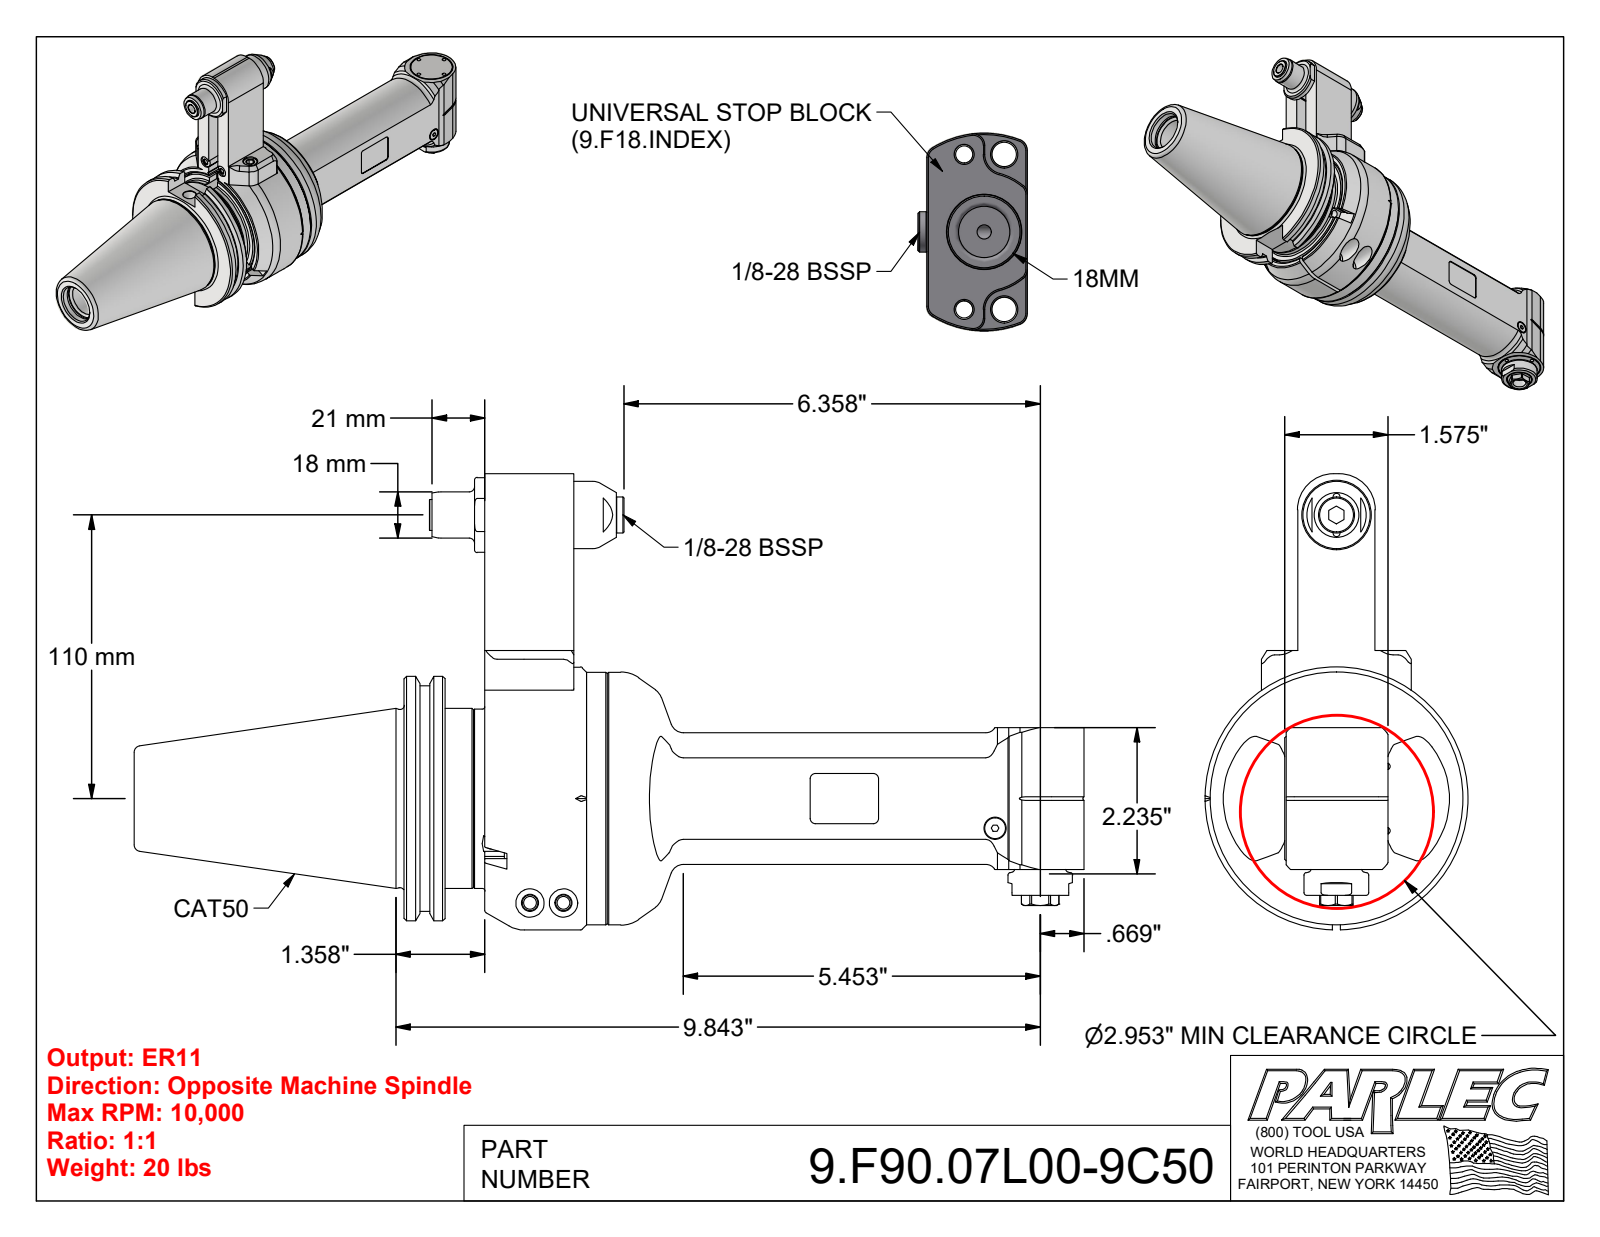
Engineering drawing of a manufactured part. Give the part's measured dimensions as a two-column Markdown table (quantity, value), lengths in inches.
| quantity | value |
| --- | --- |
| part name | 9.F90.07L00-9C50; 9_F90_07L00; 9_GA11C_451 (Type 1, Cat50, 110mm) |
| STEP written by | Autodesk Inventor 2022 (AUTOMOTIVE_DESIGN) |
| units | inches |
| bodies | 5 solids, 552 faces (232 planar, 160 cylindrical, 160 other) |
| overall size | 14.512 × 6.968 × 4.016 |
| volume | 77.75 in³ |
| surface area | 268.1 in² |
| round holes (diameter × count) | 0.197 × 7, 0.102 × 6, 0.256 × 3, 0.315 × 3, 0.13 × 2, 0.165 × 2, 0.409 × 2, 0.433 × 2, 0.492 × 2, 0.118 × 1, 0.276 × 1, 0.295 × 1 |
| round bosses / shafts (diameter × count) | 0.709 × 3, 0.472 × 2, 0.394 × 2, 0.098 × 2, 4.016 × 1, 3.875 × 1, 3.858 × 1, 3.594 × 1 |
| partial cylindrical surfaces (radius × count) | 0.039 × 14, 0.079 × 12, 0.118 × 6, 0.157 × 4, 0.016 × 2, 0.02 × 2, 0.315 × 2, 0.551 × 2 |
| main face-to-face distances | 1.26, 0.197, 1.575, 1.378, 1.555, 2.163, 0.904, 0.61, 0.335, 2.789 |
| hole center spacings | 0.492, 0.696, 0.276, 0.984, 1.994, 2.11, 2.383, 2.657 |
